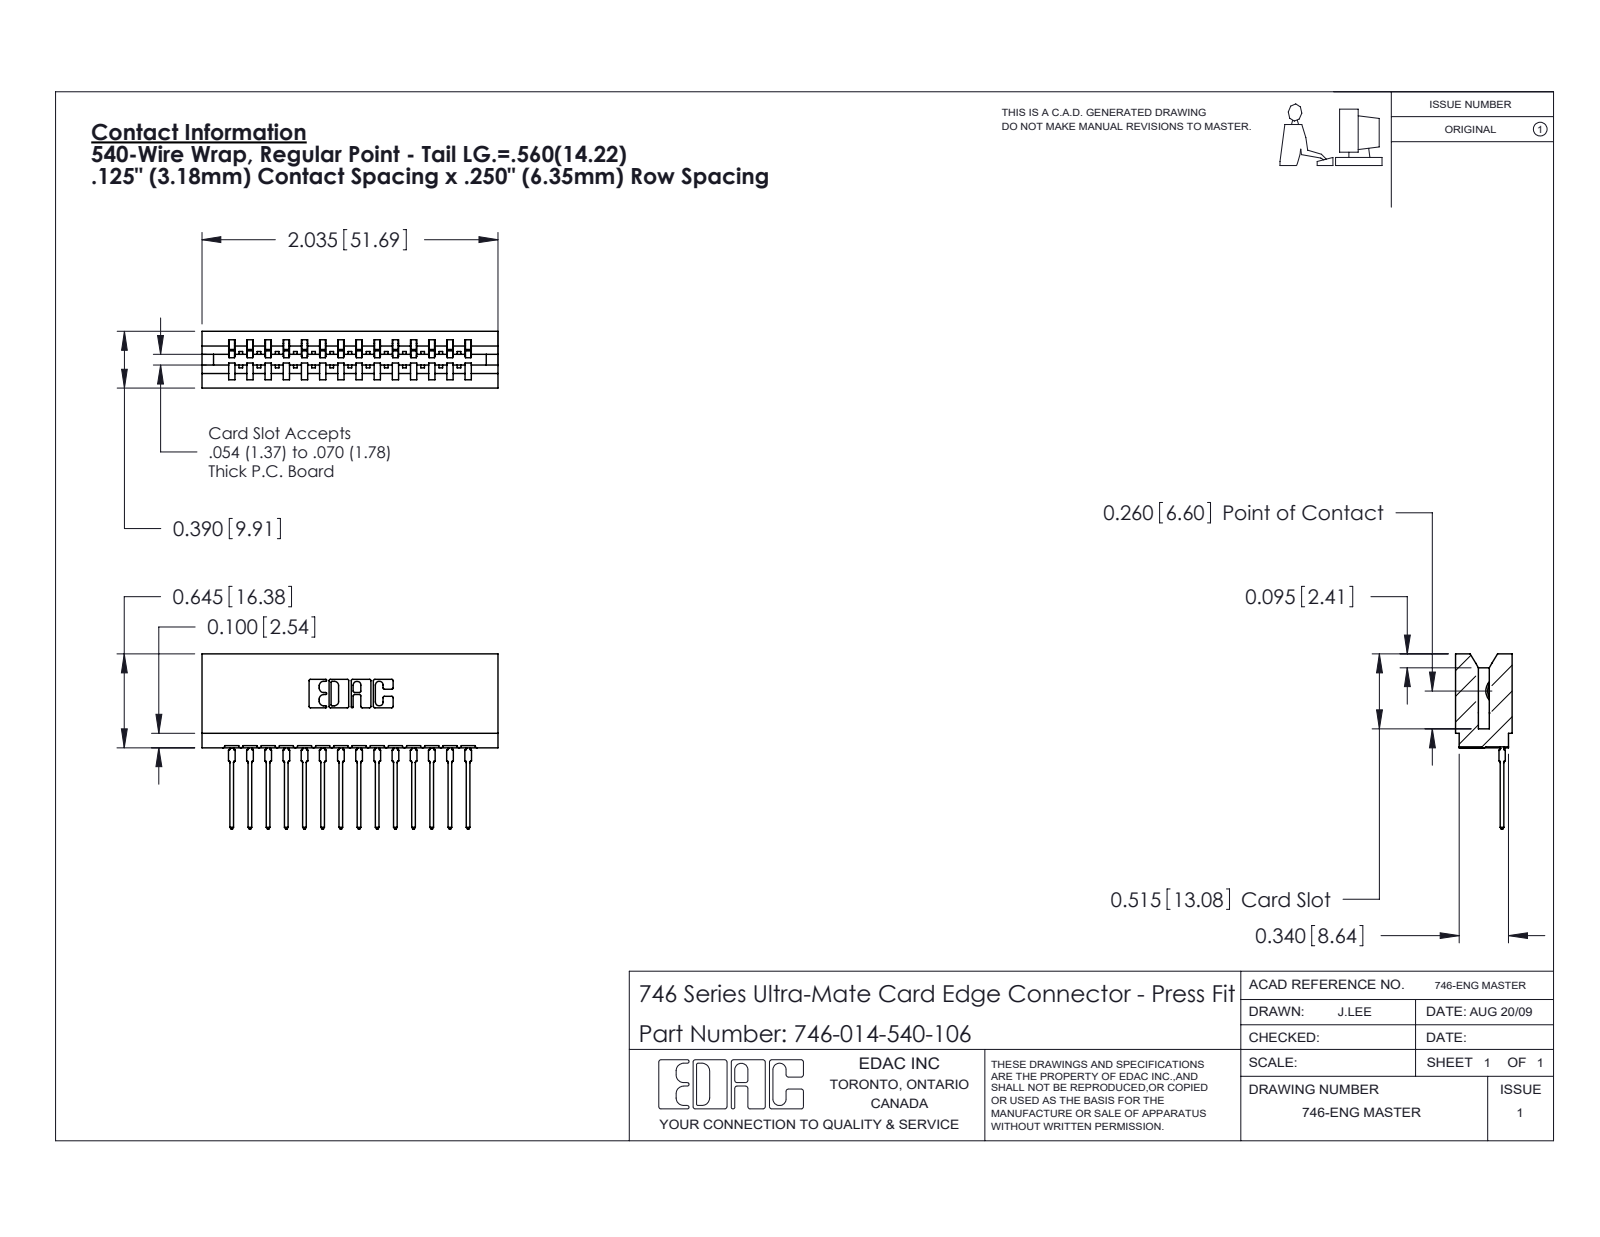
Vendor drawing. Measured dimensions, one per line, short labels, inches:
name: 746-292-001_540; 746 Part_.515 Slot Depth - 06; 746-014-540-106
written by: SolidWorks 2020 (CONFIG_CONTROL_DESIGN)
unit: in
bodies: 15 solids, 1610 faces (938 planar, 308 cylindrical, 364 other)
size: 2.035 × 1.204 × 0.39
volume: 0.342 in³; area: 12.43 in²
rounds: 28× R0.021, 22× R0.01, 15× R0.015, 6× R0.007, 6× R0.031, 4× R0.005, 4× R0.011, 3× R0.026
face distances: 0.25, 0.333, 0.057, 0.5, 0.39, 0.125, 0.083, 0.042, 0.208, 0.375
